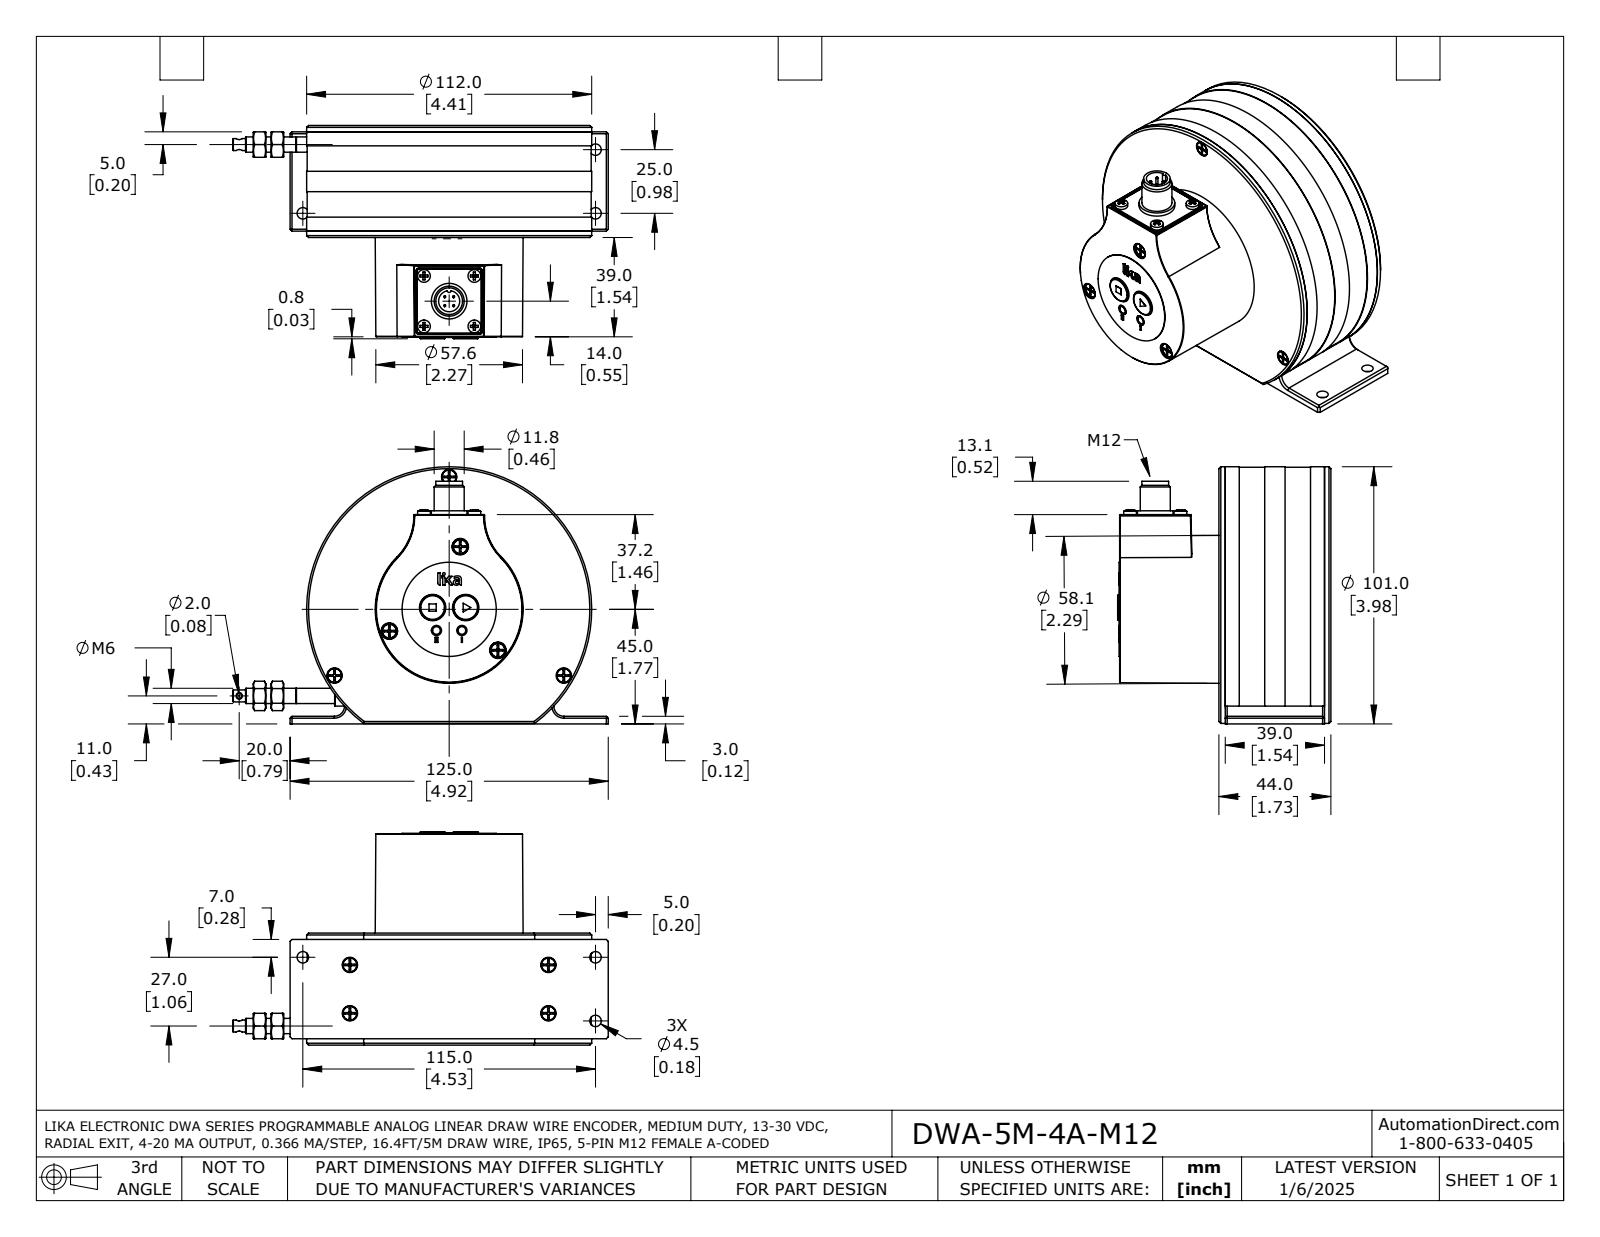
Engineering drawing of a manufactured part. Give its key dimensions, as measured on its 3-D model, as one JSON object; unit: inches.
{"part_name": "DWA-5M-4A-M12", "step_written_by": "SolidWorks 2021 (AUTOMOTIVE_DESIGN)", "units": "inches", "bodies": {"solids": 31, "faces": 2026, "planar": 1231, "cylindrical": 397, "other": 398}, "overall_size": [5.807, 3.976, 3.299], "volume_in3": 12.98, "surface_area_in2": 185.4, "round_holes": [[0.098, 13], [0.126, 7], [0.236, 7], [0.079, 5], [0.157, 4], [0.177, 4], [0.059, 2], [0.063, 2], [0.118, 2], [0.315, 2], [0.374, 2], [0.197, 1]], "round_bosses_or_shafts": [[0.118, 11], [0.197, 4], [0.098, 4], [0.055, 4], [0.031, 4], [0.157, 2], [4.409, 1], [2.205, 1]], "partial_cylinders_radius": [[0.008, 45], [0.007, 33], [0.02, 6], [0.03, 5], [0.157, 2], [0.034, 1], [0.035, 1], [0.036, 1]], "face_to_face_distances": [0.02, 1.634, 0.098, 0.079, 1.535, 0.118, 1.654, 1.319, 1.732, 0.059], "hole_center_spacings": [0.984, 1.705, 0.648, 0.738, 0.509, 0.728, 0.827, 1.039]}
